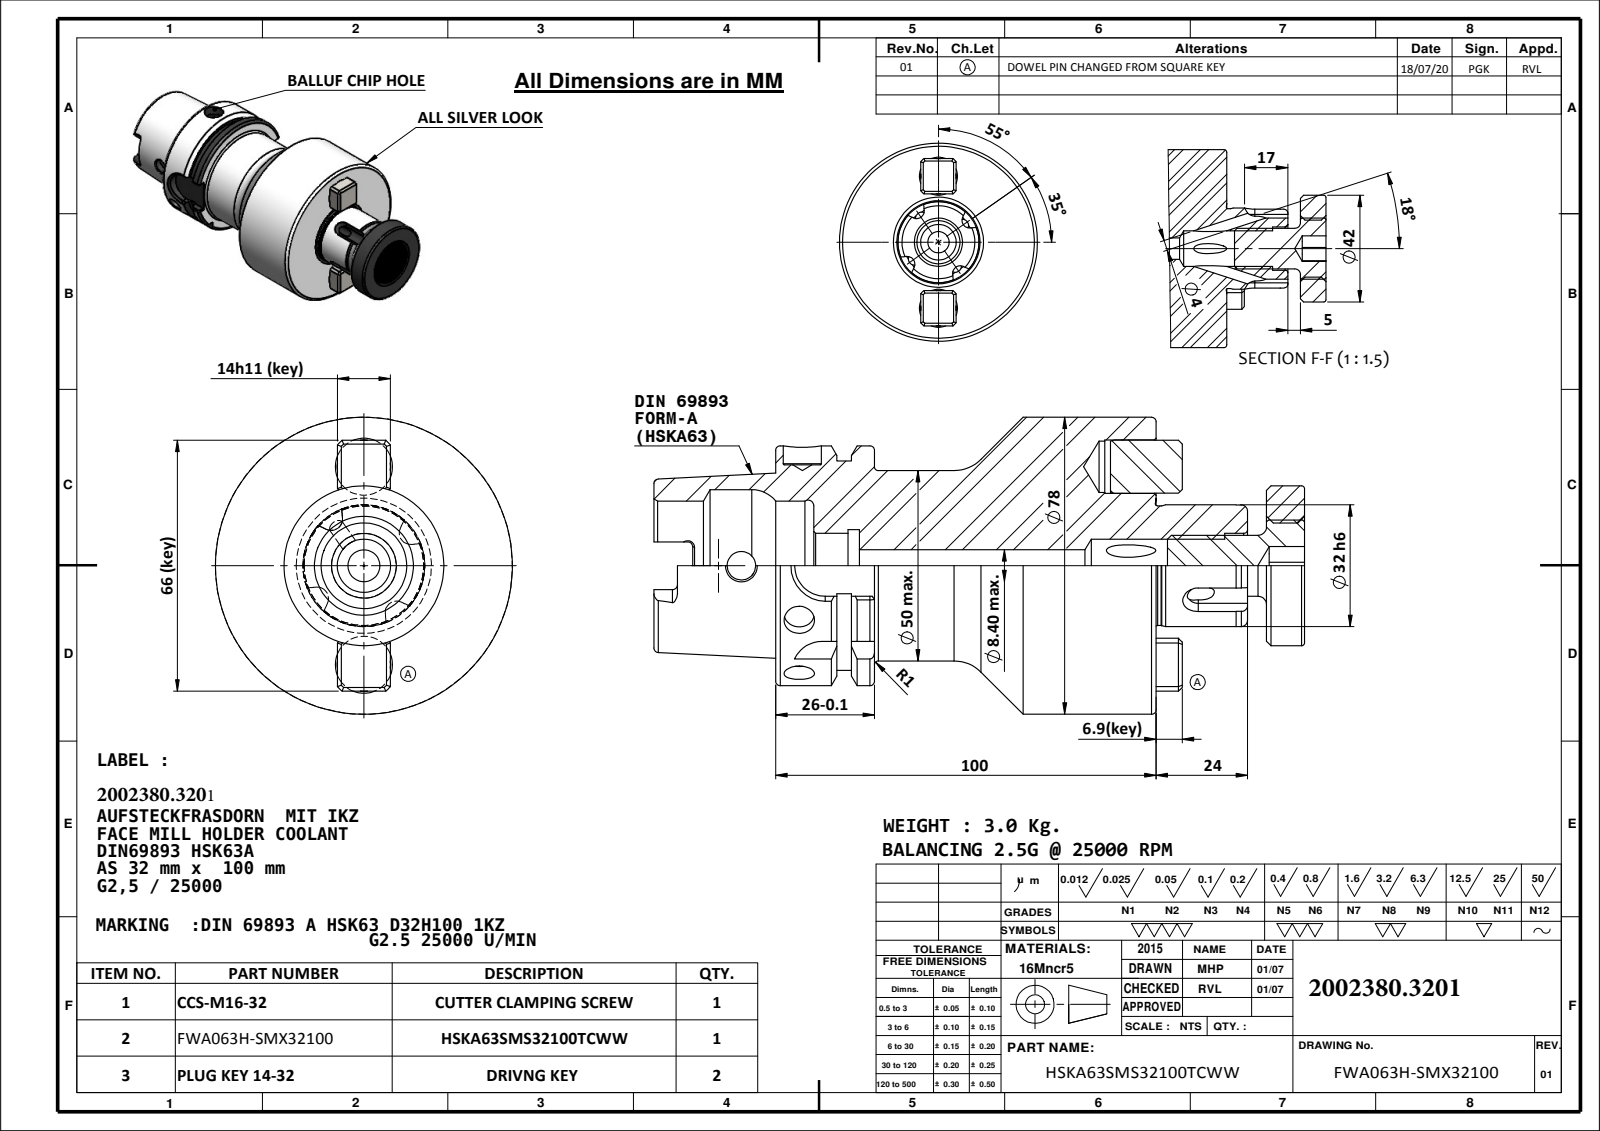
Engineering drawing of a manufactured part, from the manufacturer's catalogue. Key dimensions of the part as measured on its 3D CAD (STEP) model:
Part name (STEP PRODUCT): CCS-M16-32-2.IGS; CCS-M16-32.IGS; HSKA63SMS32100TCWW.IGS; 9163A-AS532100 (+1 more)
STEP written by: SolidWorks 2018 (AUTOMOTIVE_DESIGN)
Units: millimetres
Bodies: 5 solids, 365 faces (0 planar, 0 cylindrical, 365 other)
Overall size (bounding box): 170.95 × 78 × 78
Volume: 369 788 mm³ · Surface area: 58 646 mm²
